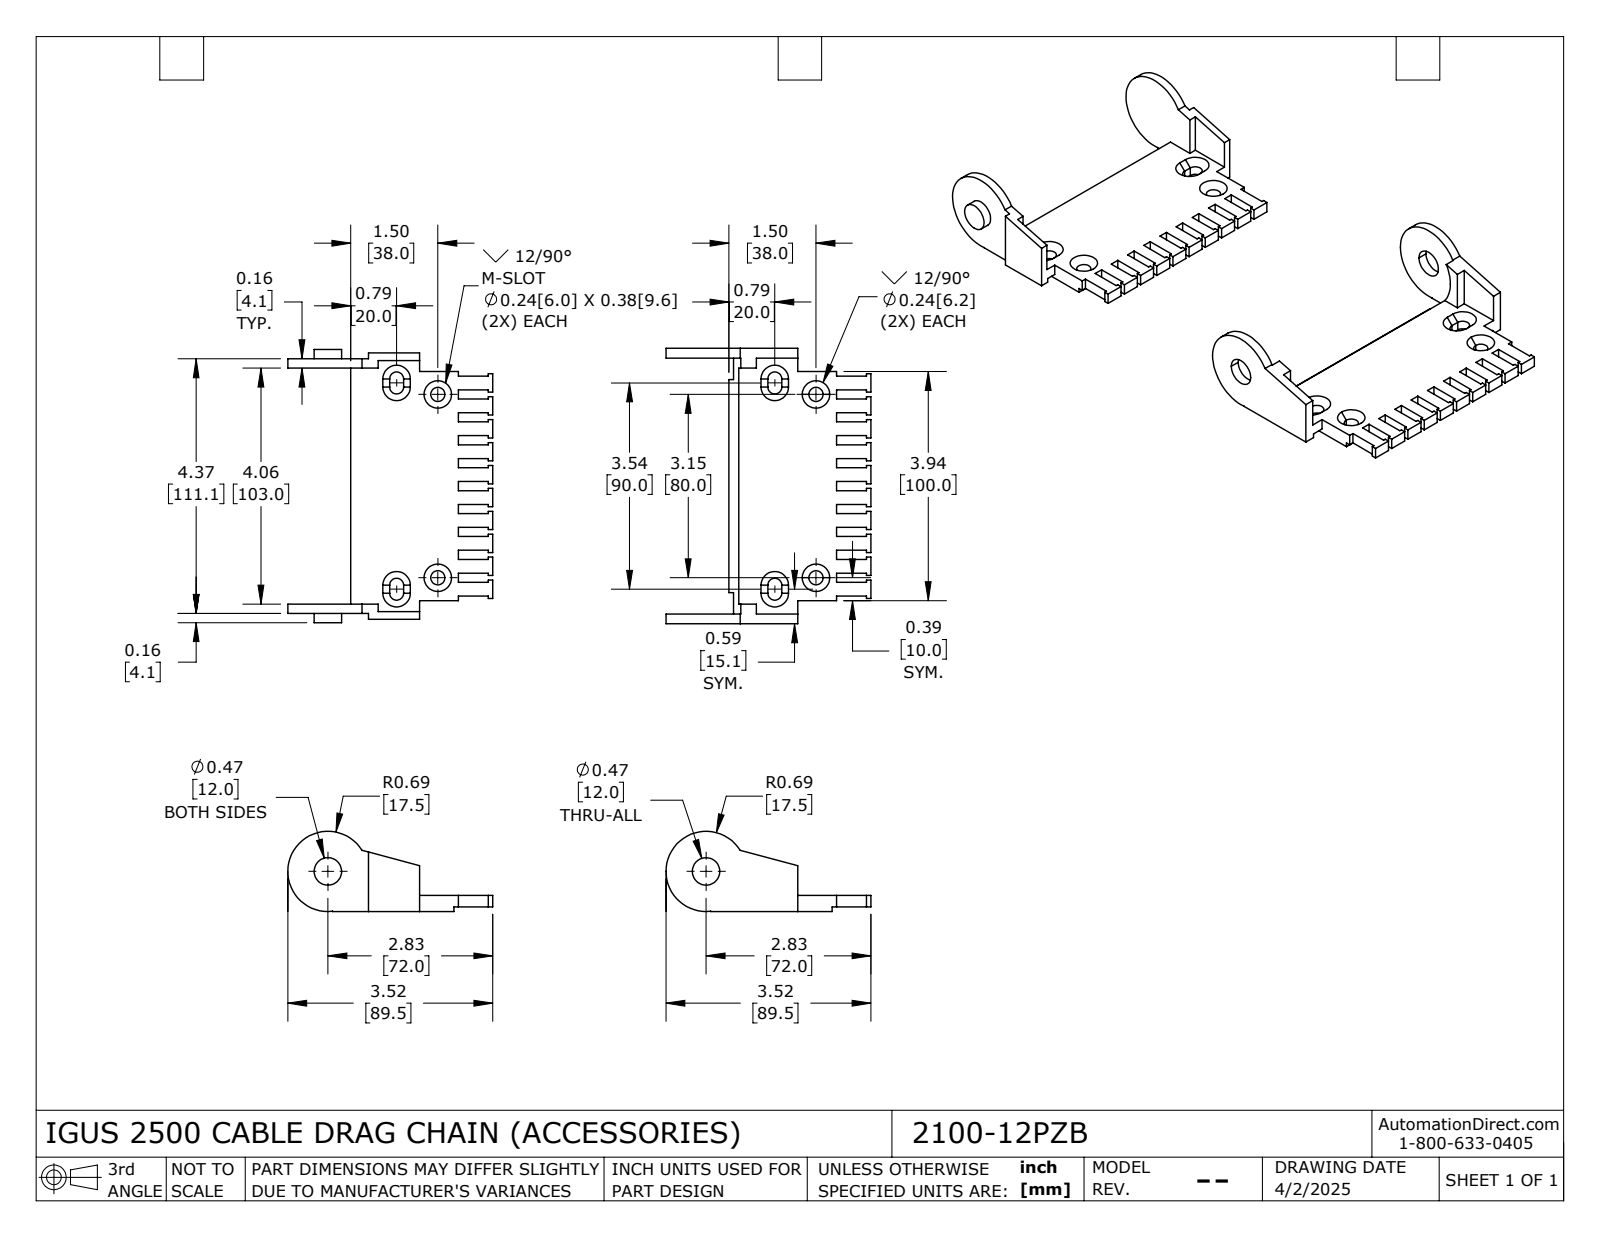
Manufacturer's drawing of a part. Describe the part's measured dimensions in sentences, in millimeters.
The part is named "2100-12PZB". Its 3-D file was written by "SolidWorks 2024 (AUTOMOTIVE_DESIGN)". It is 2 solids with 291 faces: 248 planar, 29 cylindrical and 14 other. Overall it measures 254.6 by 120.2 by 35 millimeters. Its volume is 99 966 cubic millimeters and its surface area 47 382 square millimeters. Round holes: 4 of diameter 6.2, 1 of diameter 12. Round bosses or shafts: 1 of diameter 12. Partial cylindrical surfaces (rounded edges, fillets, slot ends): 8 of radius 3.05, 2 of radius 17.5, 1 of radius 17.7. The main face-to-face distances are 7, 2, 4.3, 111.6, 5, 8.6, 115.9, 107.3, 4.55, 115.65. The hole center spacings are 80, 165.1, 183.46.
